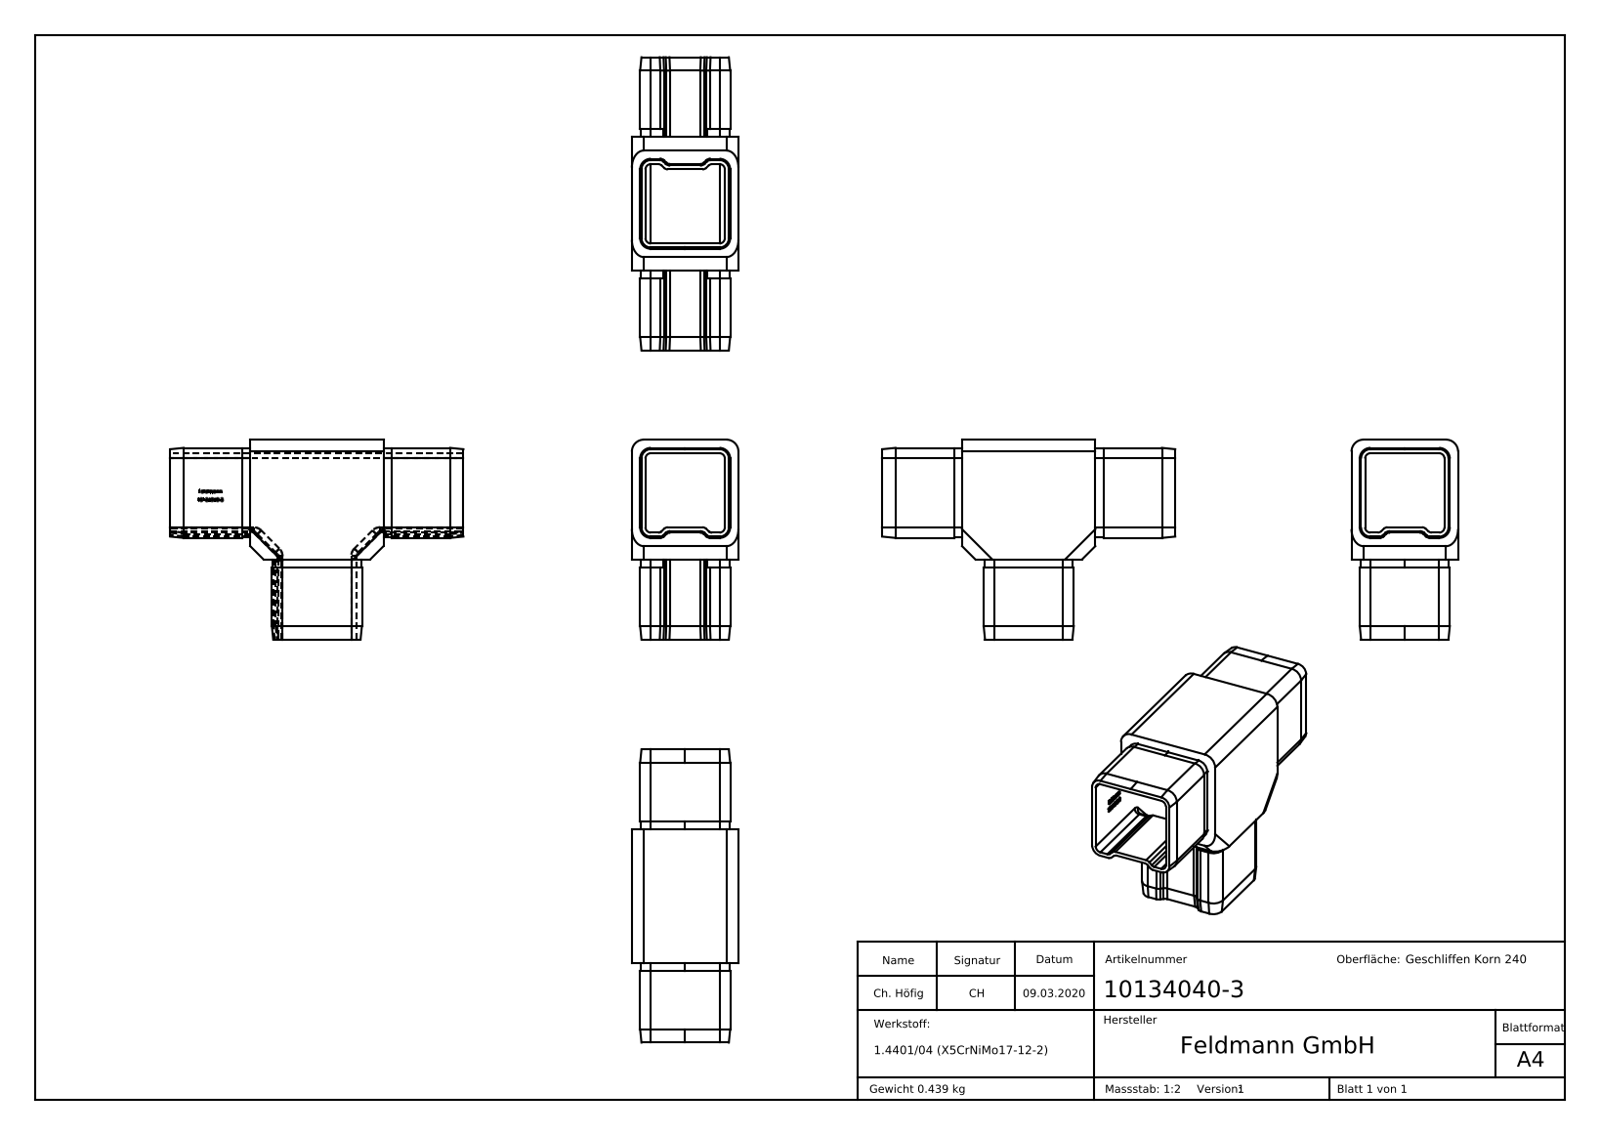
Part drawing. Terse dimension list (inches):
name: 10134040-3
written by: SolidWorks 2015 (CONFIG_CONTROL_DESIGN)
unit: in
bodies: 1 solid, 487 faces (259 planar, 95 cylindrical, 133 other)
size: 4.331 × 2.953 × 1.575
volume: 3.348 in³; area: 57.62 in²
rounds: 52× R0.079, 8× R0.146, 8× R0.157, 6× R0.177, 2× R0.059
face distances: 0.079, 1.173, 0.201, 1.252, 1.374, 0.122, 1.453, 1.331, 1.575, 1.571
